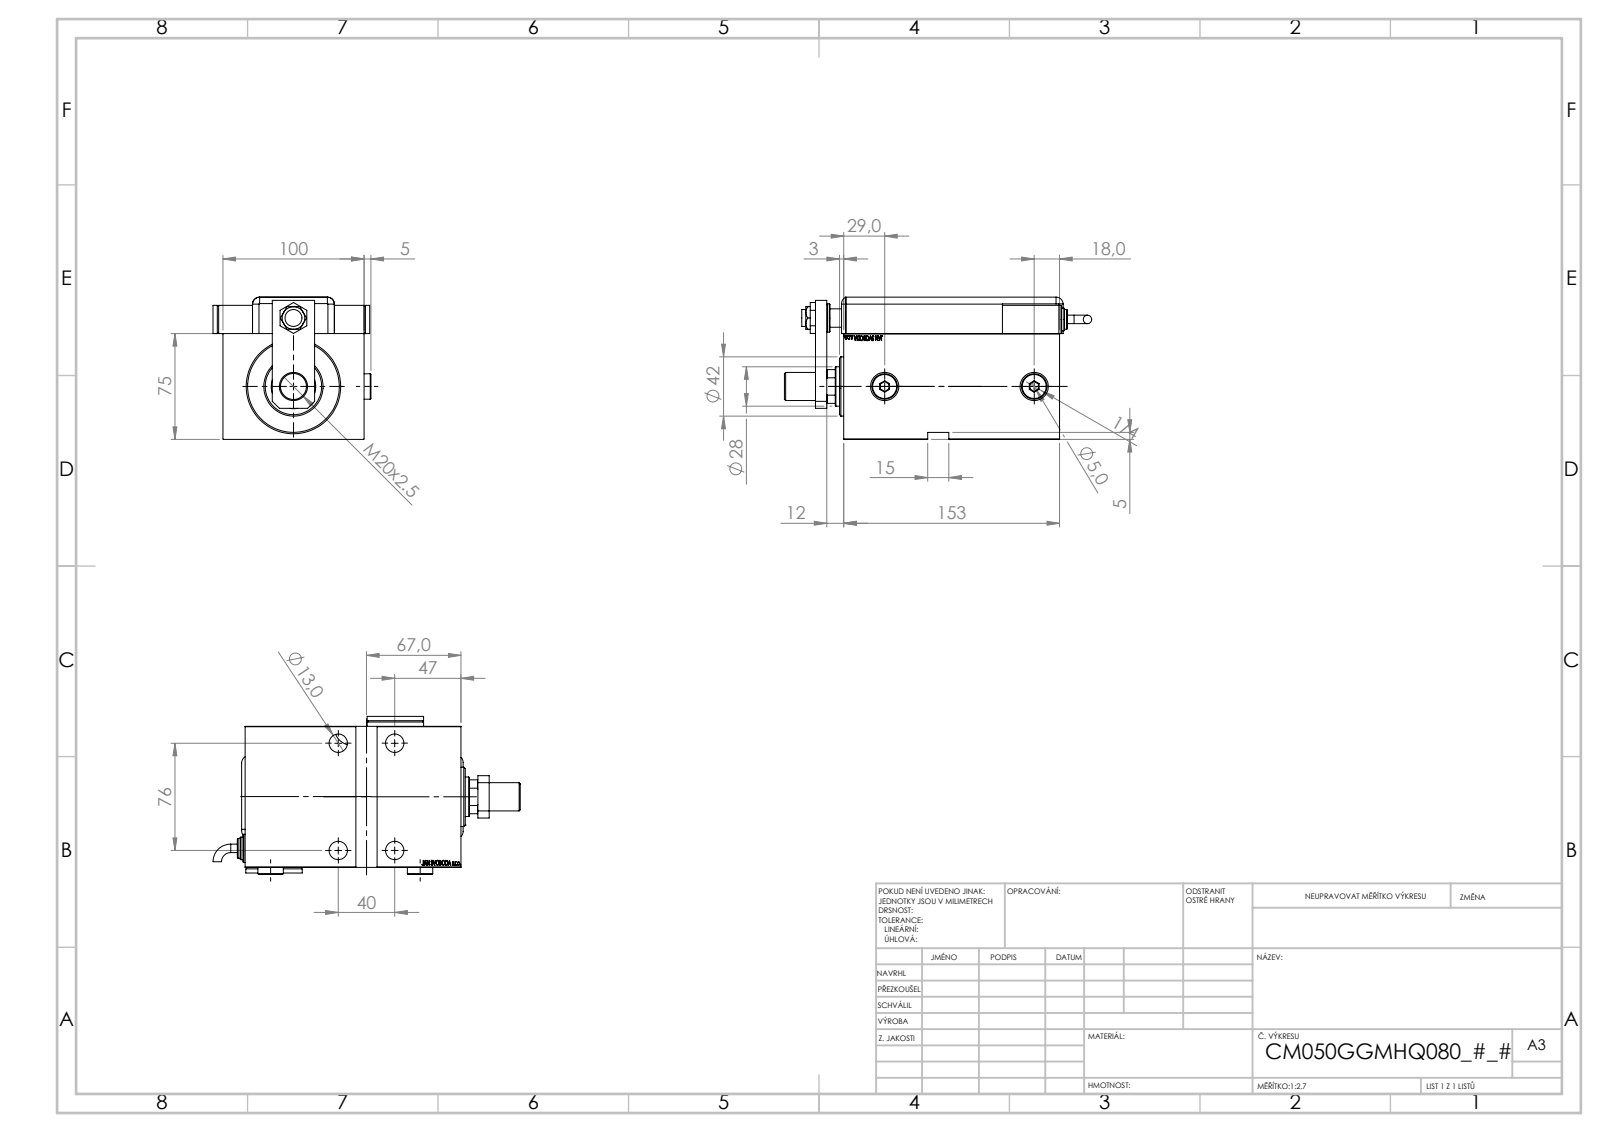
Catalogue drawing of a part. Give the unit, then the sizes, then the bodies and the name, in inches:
Units: inches
Overall size (bounding box): 8.573 × 4.406 × 3.969
Round holes (diameter × count): ⌀0.512 ×5, ⌀0.748 ×4, ⌀0.787 ×3, ⌀0.157 ×2, ⌀0.197 ×2, ⌀0.315 ×2, ⌀0.518 ×2, ⌀0.472 ×1, ⌀0.551 ×1, ⌀0.728 ×1, ⌀1.102 ×1, ⌀1.24 ×1
Round bosses / shafts (diameter × count): ⌀0.787 ×3, ⌀0.709 ×3, ⌀0.63 ×2, ⌀0.551 ×2, ⌀0.236 ×2, ⌀1.654 ×1
Partial cylindrical surfaces — rounded edges, fillets, slot ends (radius × count): R0.197 ×9, R0.394 ×1, R0.531 ×1
Main face-to-face distances: 0.118, 2.953, 3.937, 3.969, 1.016, 6.024, 0.197, 0.551, 0.898, 3.85
Hole centre spacings: 1.575, 1.858, 2.41, 2.992, 3.263, 3.381, 3.606, 0.787
Volume: 69.87 in³ · Surface area: 321.3 in²
Bodies: 16 solids, 1294 faces (652 planar, 115 cylindrical, 527 other)
Part name (STEP PRODUCT): V450CM_MALE_METRIC; V450CM_G_VCP; V450CM_G_Body; Zatka_OIL_PORT (+7 more)
STEP written by: SolidWorks 2019 (CONFIG_CONTROL_DESIGN)
